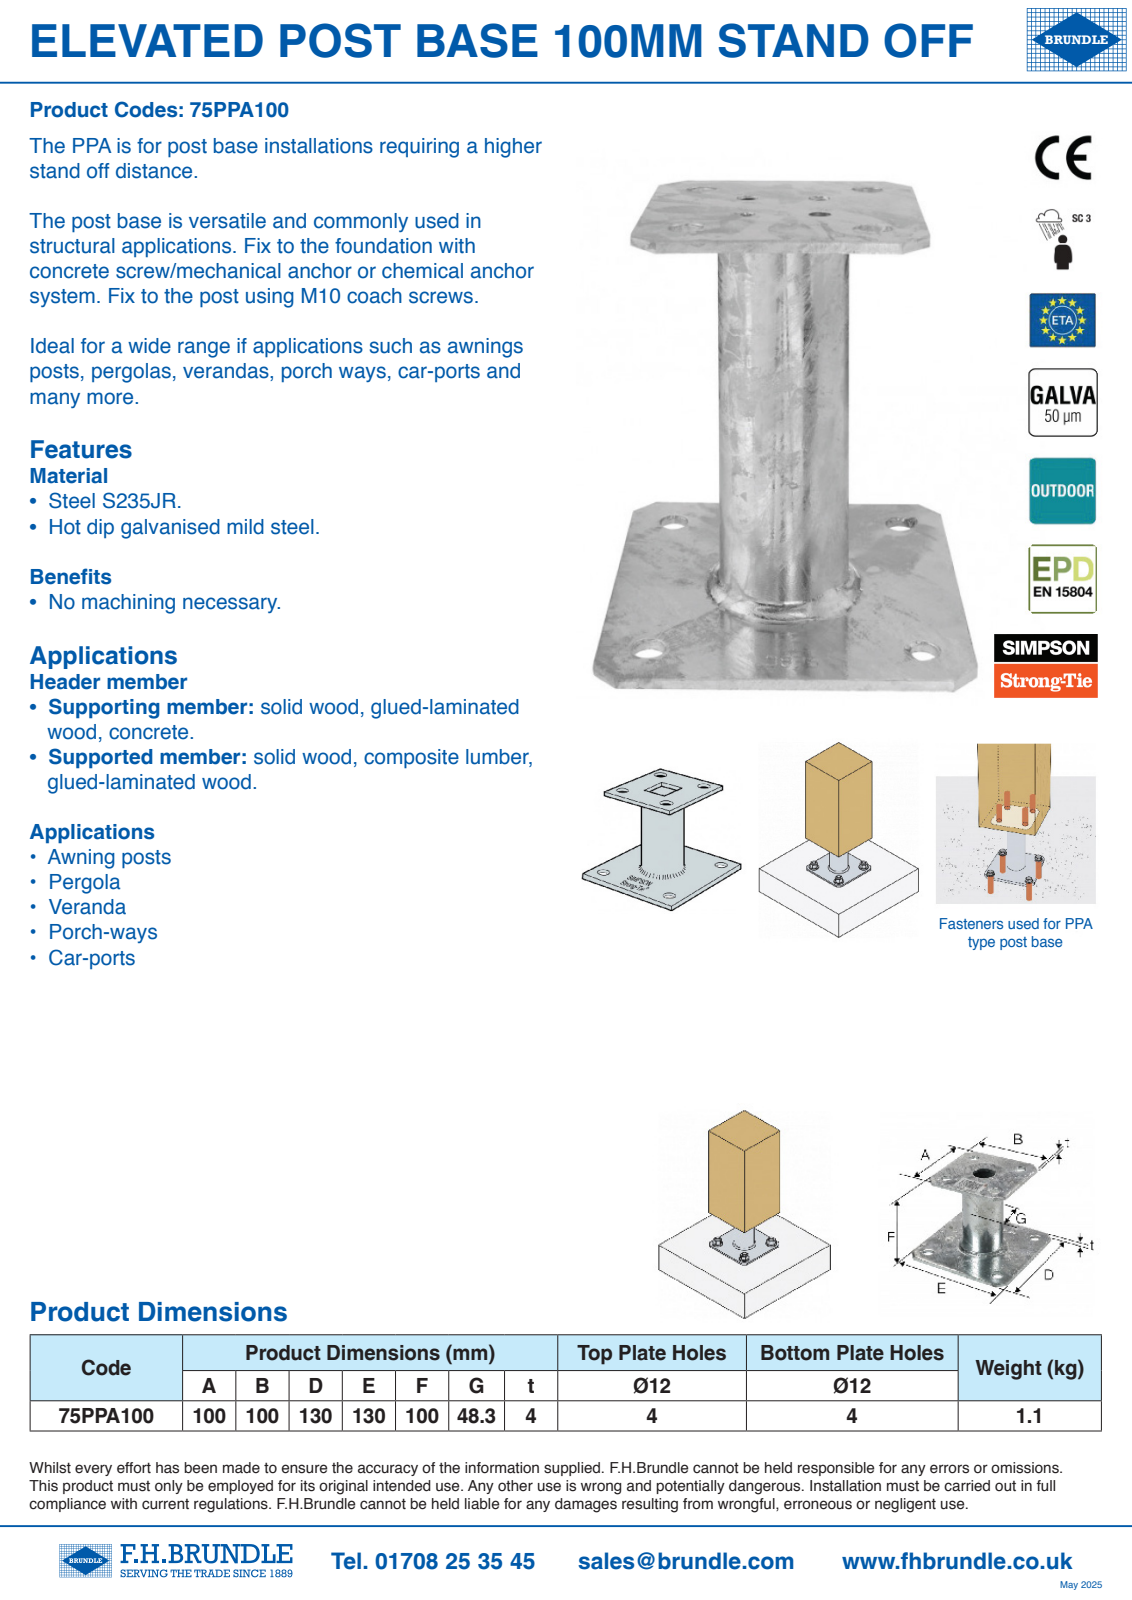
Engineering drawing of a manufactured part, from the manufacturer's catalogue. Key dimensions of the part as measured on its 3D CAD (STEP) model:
Part name (STEP PRODUCT): 75PPA100
STEP written by: SolidWorks 2023 (CONFIG_CONTROL_DESIGN)
Units: millimetres
Bodies: 3 solids, 50 faces (14 planar, 36 cylindrical, 0 other)
Overall size (bounding box): 130 × 130 × 100
Volume: 135 466 mm³ · Surface area: 84 071 mm²
Round holes (diameter × count): ⌀12 ×8, ⌀8 ×4, ⌀43.3 ×1
Round bosses / shafts (diameter × count): ⌀48.3 ×1
Main face-to-face distances: 4, 96, 100, 92, 15, 115, 130
Hole centre spacings: 49.04, 69.1, 80.41, 18.89, 21.21, 26.36, 26.72, 45.25
